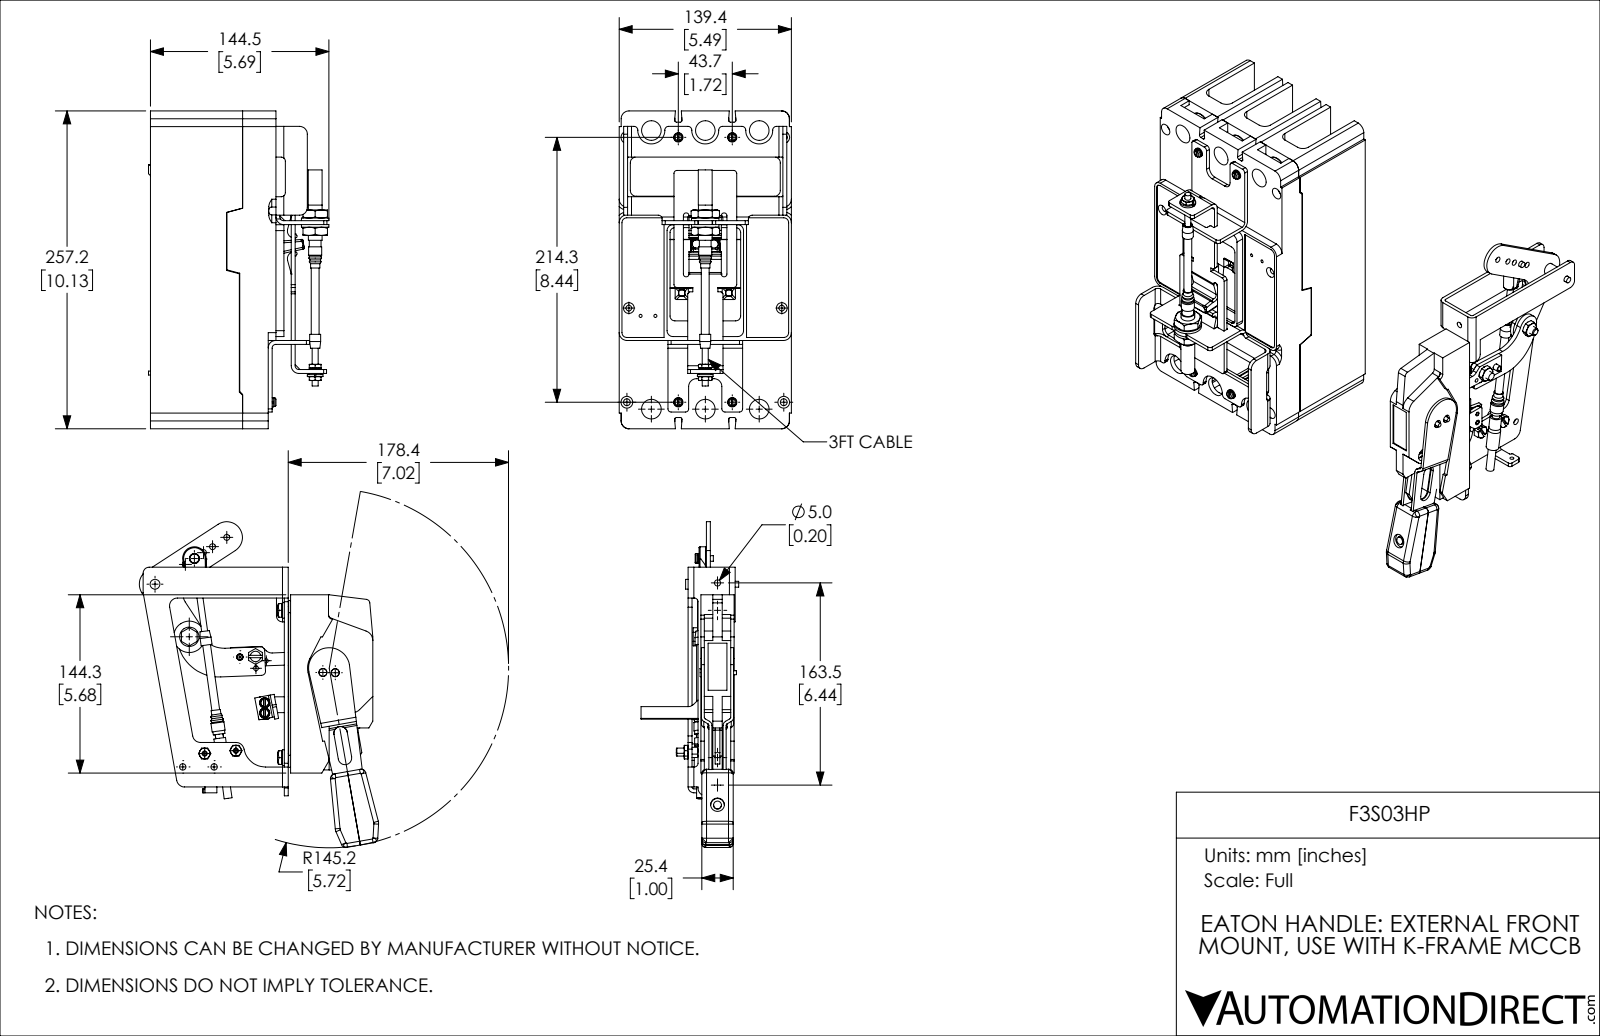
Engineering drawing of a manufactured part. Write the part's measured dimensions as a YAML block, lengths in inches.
part_name: "F3S03HP; F3S03HP_HANDLE; F3S03HP_BREAKER"
step_written_by: "SolidWorks 2019 (CONFIG_CONTROL_DESIGN)"
units: inches
bodies: {solids: 81, faces: 2972, planar: 1428, cylindrical: 1143, other: 401}
overall_size: [14.165, 10.378, 7.627]
volume: 182.3
surface_area: 888.8
round_holes:
  - {diameter: 0.219, count: 8}
  - {diameter: 0.203, count: 6}
  - {diameter: 0.228, count: 6}
  - {diameter: 0.625, count: 6}
  - {diameter: 0.188, count: 5}
  - {diameter: 0.196, count: 5}
  - {diameter: 0.281, count: 5}
  - {diameter: 0.375, count: 5}
  - {diameter: 0.438, count: 5}
  - {diameter: 0.168, count: 4}
  - {diameter: 0.25, count: 4}
  - {diameter: 0.5, count: 4}
round_bosses_or_shafts:
  - {diameter: 0.25, count: 9}
  - {diameter: 0.338, count: 6}
  - {diameter: 0.375, count: 5}
  - {diameter: 0.5, count: 4}
  - {diameter: 0.297, count: 4}
  - {diameter: 0.27, count: 4}
  - {diameter: 0.138, count: 4}
  - {diameter: 0.394, count: 3}
partial_cylinders:
  - {radius: 0.062, count: 109}
  - {radius: 0.125, count: 53}
  - {radius: 0.25, count: 50}
  - {radius: 0.032, count: 22}
  - {radius: 0.156, count: 18}
  - {radius: 0.1, count: 16}
  - {radius: 0.188, count: 16}
  - {radius: 0.031, count: 15}
face_to_face_distances: [0.125, 5.49, 0.249, 2.906, 1.062, 3.719, 0.813, 0.032, 4, 0.156]
hole_center_spacings: [1.719, 8.17, 7.907, 8.7, 9.04, 0.531, 1.141, 1.141]
